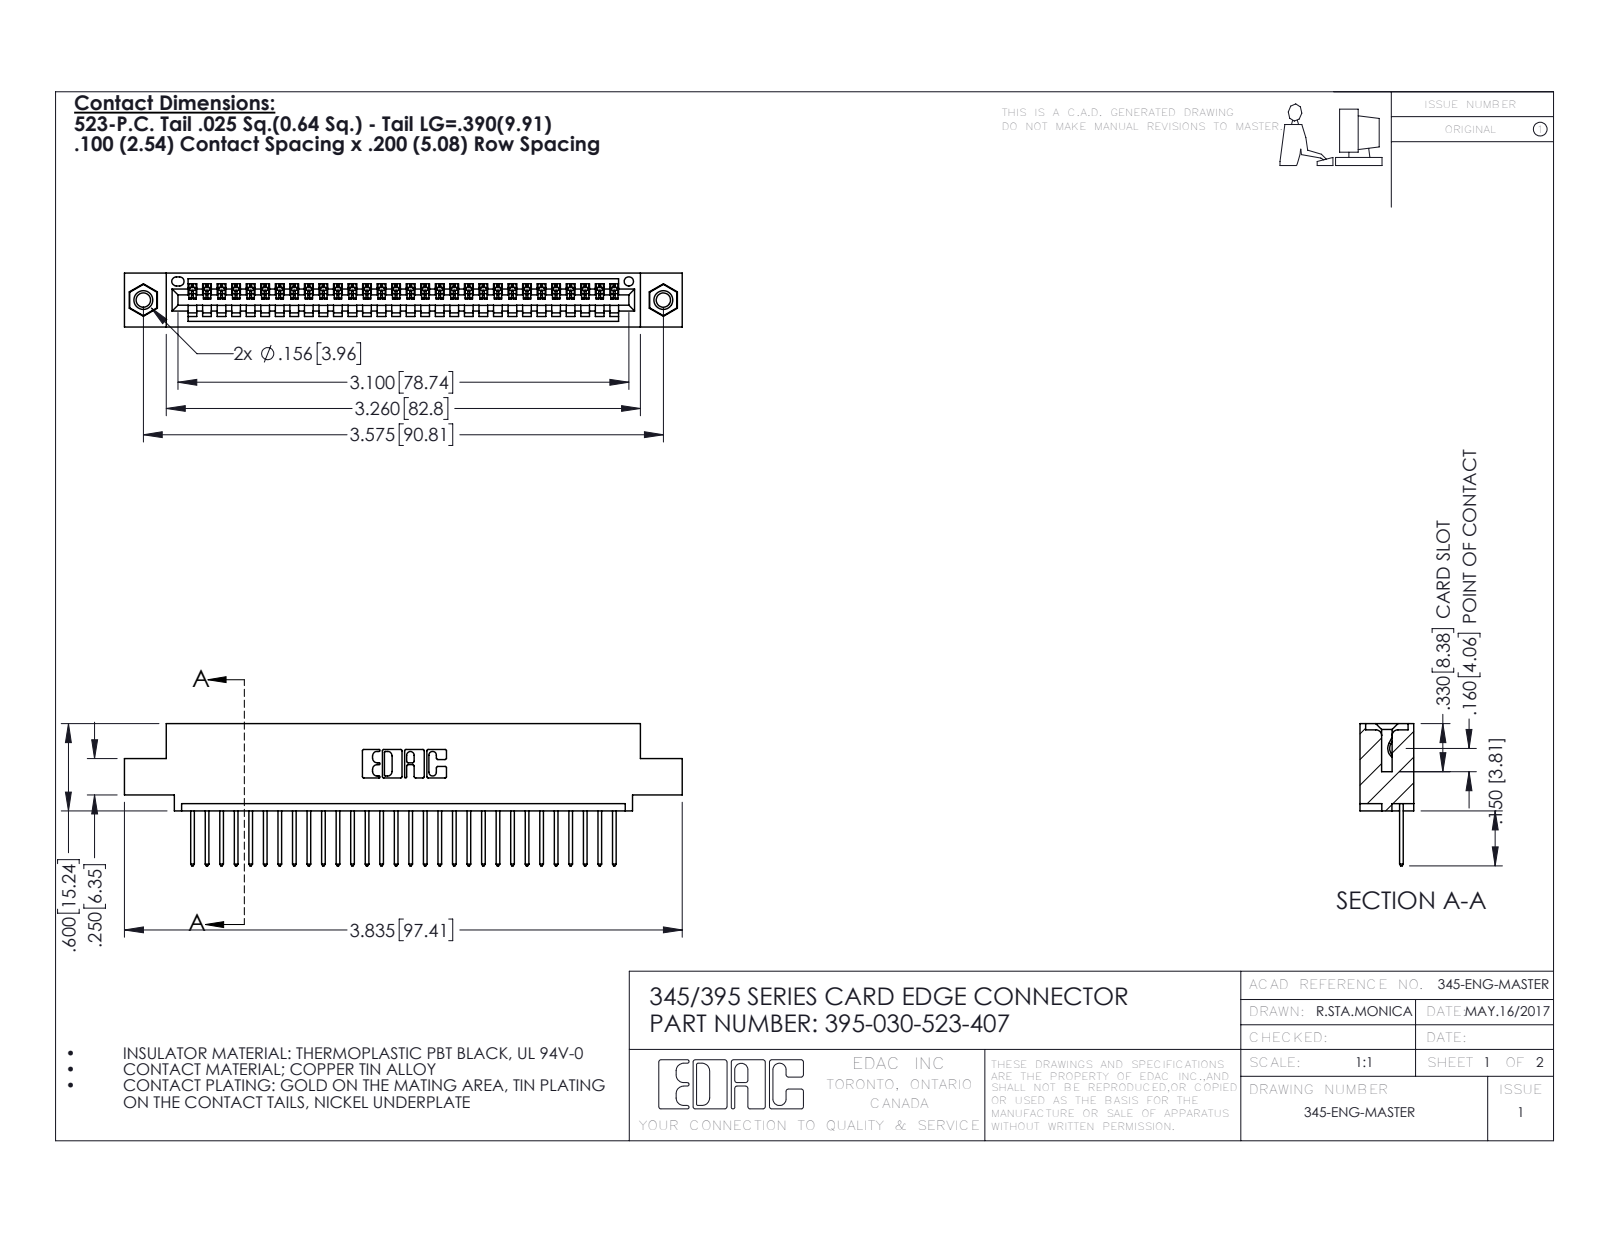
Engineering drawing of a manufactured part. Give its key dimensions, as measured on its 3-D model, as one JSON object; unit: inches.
{"part_name": "345-292-001_345-293-123; 395-030-523-407; 345-250-001_345-250-005-103; 345 Part_0.110 Offset - 0.156 Dia-TI", "step_written_by": "SolidWorks 2016 (CONFIG_CONTROL_DESIGN)", "units": "inches", "bodies": {"solids": 33, "faces": 1930, "planar": 1316, "cylindrical": 598, "other": 16}, "overall_size": [3.835, 0.977, 0.37], "volume_in3": 0.553, "surface_area_in2": 18.63, "round_holes": [[0.098, 2], [0.125, 2], [0.156, 2], [0.064, 1]], "round_bosses_or_shafts": [[0.155, 2]], "partial_cylinders_radius": [[0.006, 60], [0.01, 60], [0.01, 22], [0.007, 6], [0.031, 6], [0.026, 3], [0.031, 2], [0.04, 2]], "face_to_face_distances": [0.072, 0.298, 0.37, 0.2, 0.098, 0.272, 0.025, 0.225, 0.149, 0.072], "hole_center_spacings": [0.27, 3.34, 3.575]}
